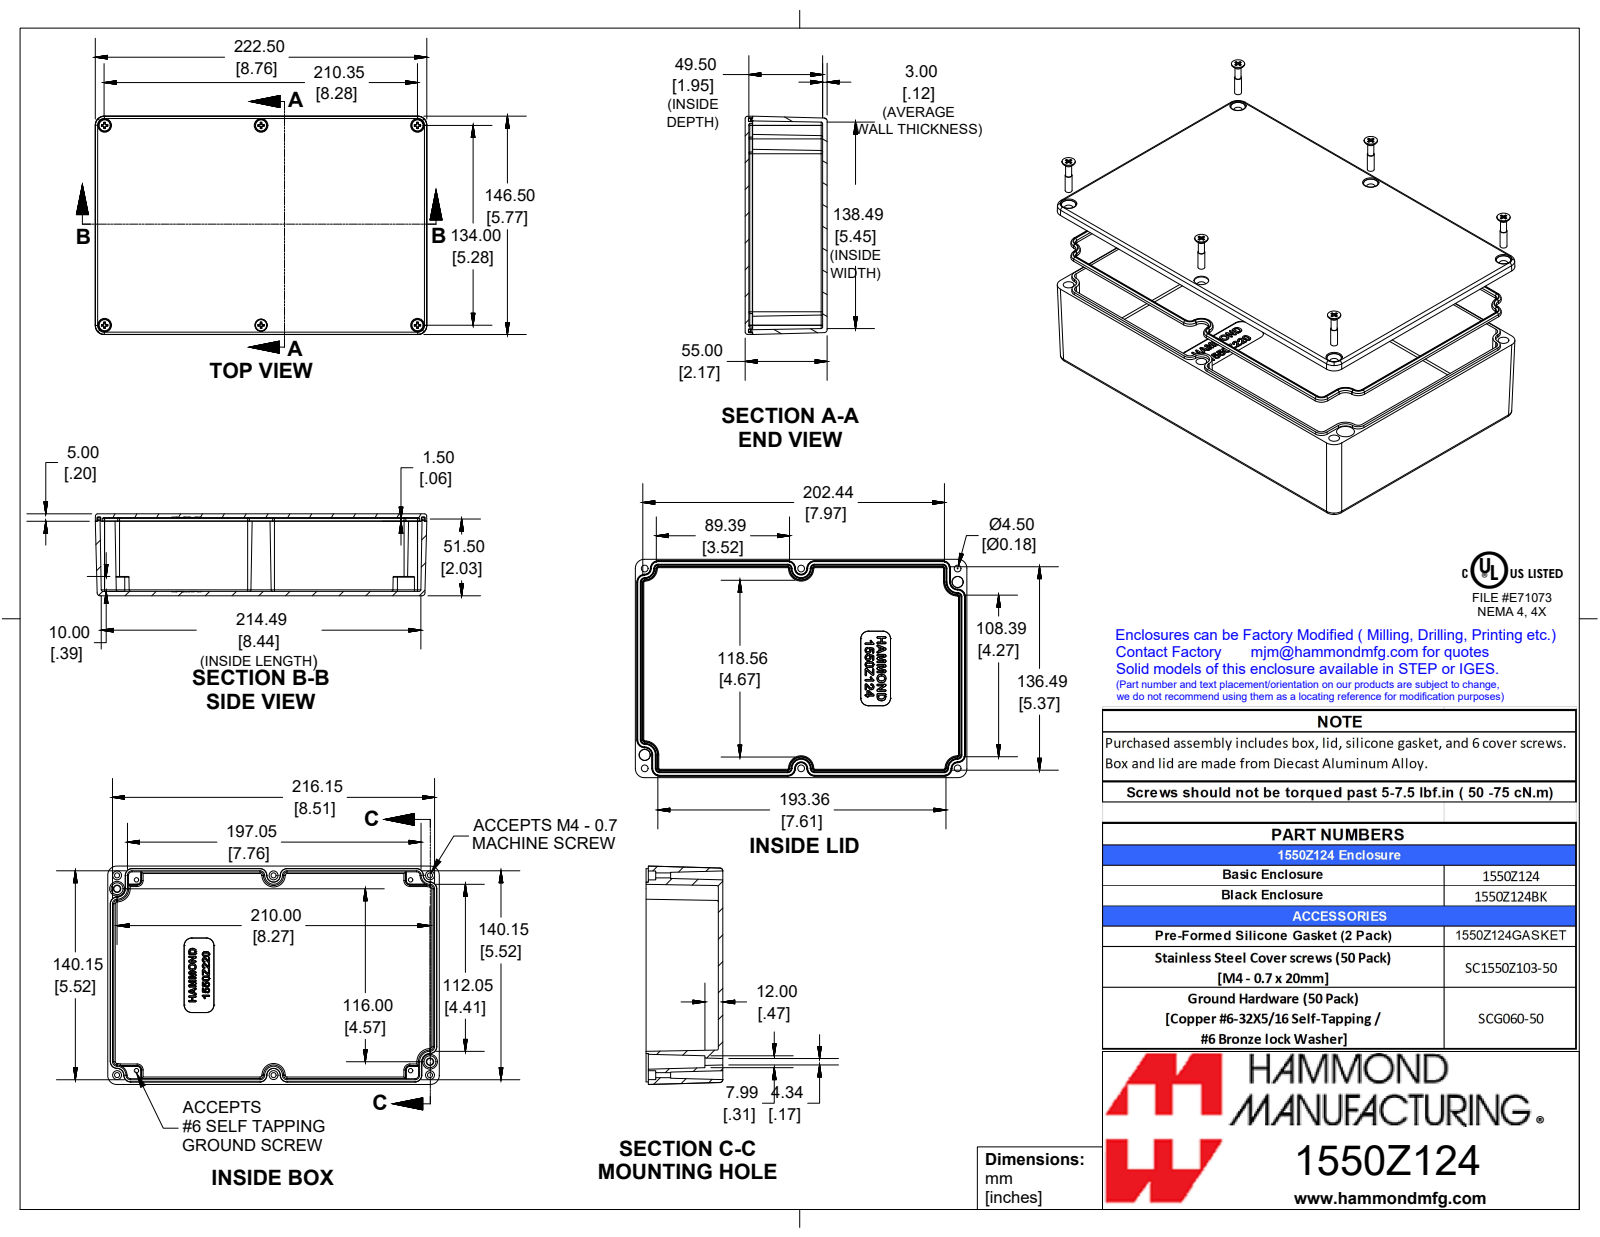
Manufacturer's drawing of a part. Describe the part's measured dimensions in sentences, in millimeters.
The part is named "1550Z124". Its 3-D file was written by "SolidWorks 2019 (AUTOMOTIVE_DESIGN)". It is 9 solids with 1693 faces: 482 planar, 310 cylindrical and 901 other. Overall it measures 222.5 by 146.5 by 55 millimeters. Its volume is 312 700 cubic millimeters and its surface area 224 100 square millimeters. Round holes: 6 of diameter 3.4, 6 of diameter 6, 4 of diameter 3. Round bosses or shafts: 6 of diameter 7.6, 6 of diameter 3.9, 6 of diameter 3.3. Partial cylindrical surfaces (rounded edges, fillets, slot ends): 44 of radius 1, 42 of radius 0.2, 28 of radius 0.3, 14 of radius 0.6, 8 of radius 6, 4 of radius 0.5, 4 of radius 1.5, 4 of radius 2. The main face-to-face distances are 2.5, 55, 3, 52, 52.5, 49.5, 5, 50, 47, 49.8. The hole center spacings are 13.3, 92, 105, 131.6, 160.1, 170.2, 197, 236.6.
